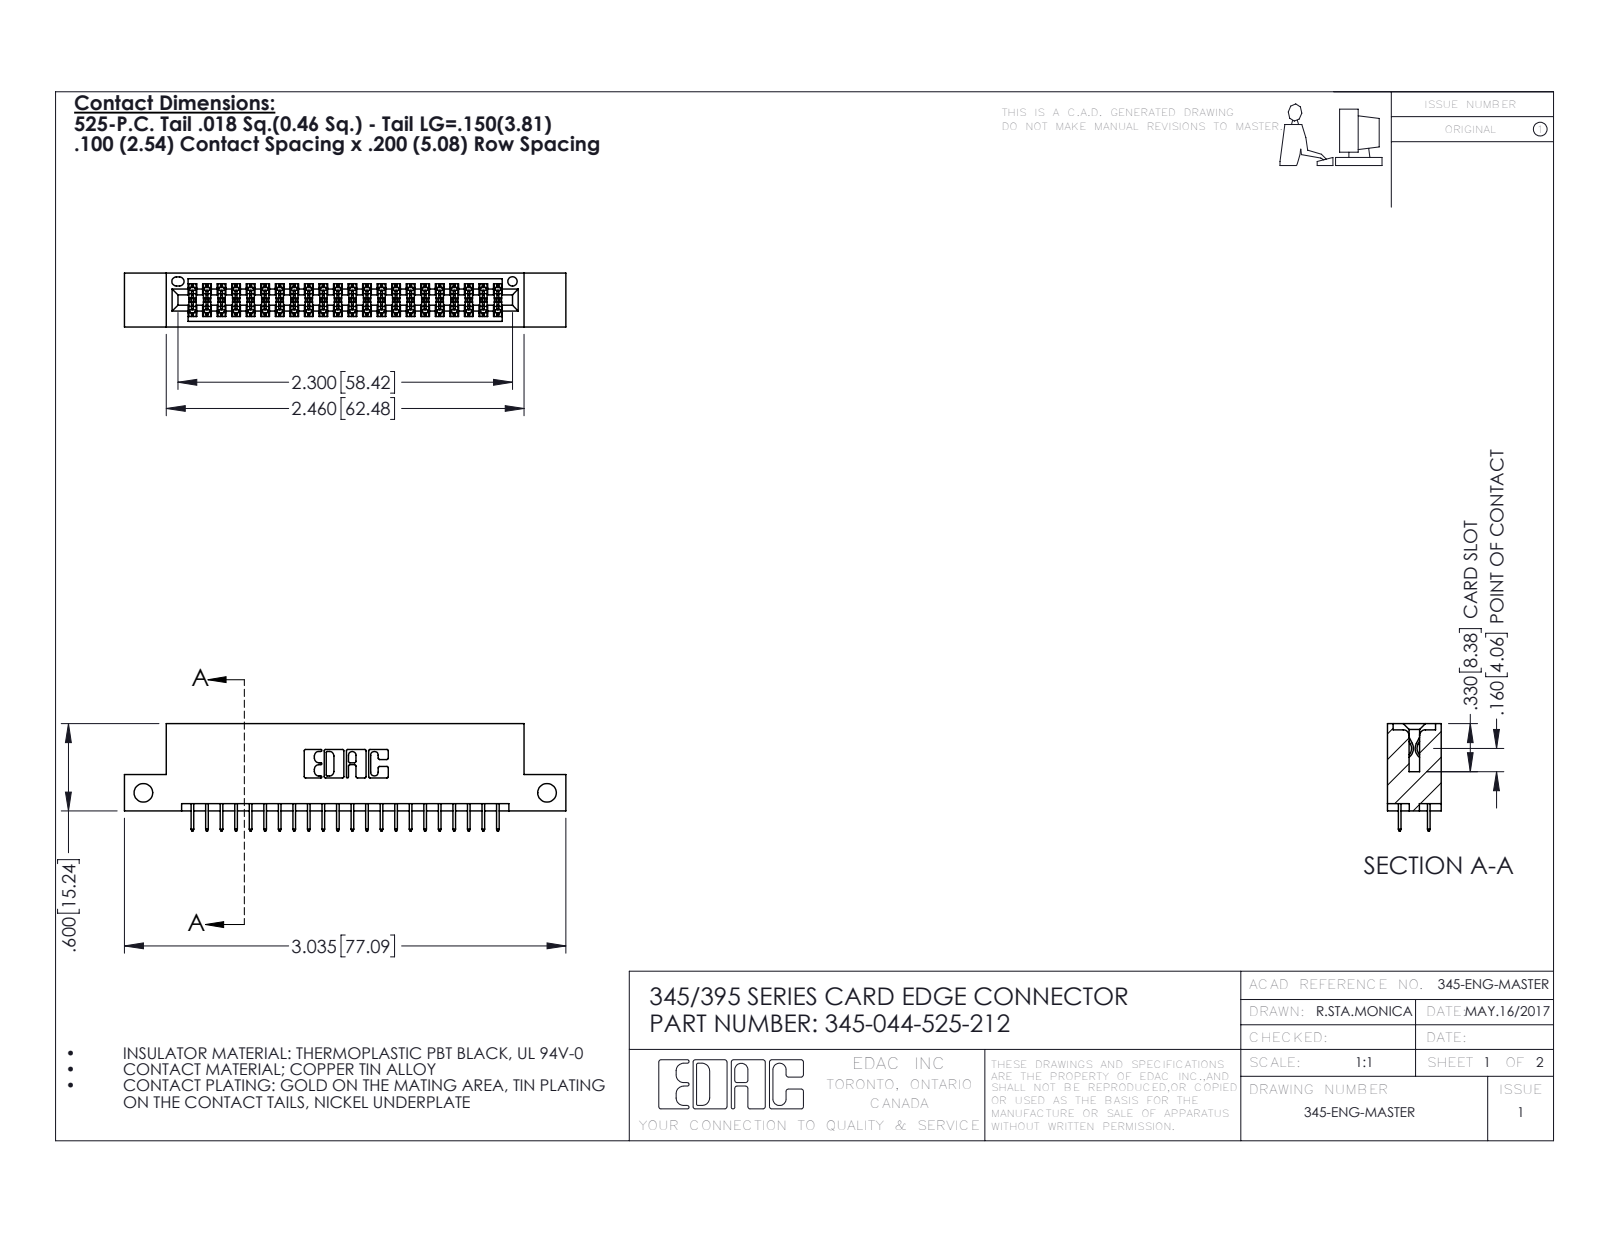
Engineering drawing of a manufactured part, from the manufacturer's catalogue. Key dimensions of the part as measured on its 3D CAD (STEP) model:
Part name (STEP PRODUCT): 345-044-525-212; 345 Part_Flush Mounting Lugs - Side Mount; 345-292-001_345-293-125
STEP written by: SolidWorks 2020 (CONFIG_CONTROL_DESIGN)
Units: inches
Bodies: 45 solids, 2502 faces (1796 planar, 706 cylindrical, 0 other)
Overall size (bounding box): 3.035 × 0.737 × 0.37
Volume: 0.436 in³ · Surface area: 15.22 in²
Round holes (diameter × count): ⌀0.128 ×2, ⌀0.064 ×1
Partial cylindrical surfaces — rounded edges, fillets, slot ends (radius × count): R0.006 ×66, R0.01 ×22, R0.007 ×6, R0.031 ×6, R0.026 ×3, R0.014 ×2, R0.019 ×2, R0.022 ×2
Main face-to-face distances: 0.298, 0.072, 0.2, 0.37, 0.098, 0.272, 0.025, 0.225, 0.072, 0.175
Hole centre spacings: 2.775
